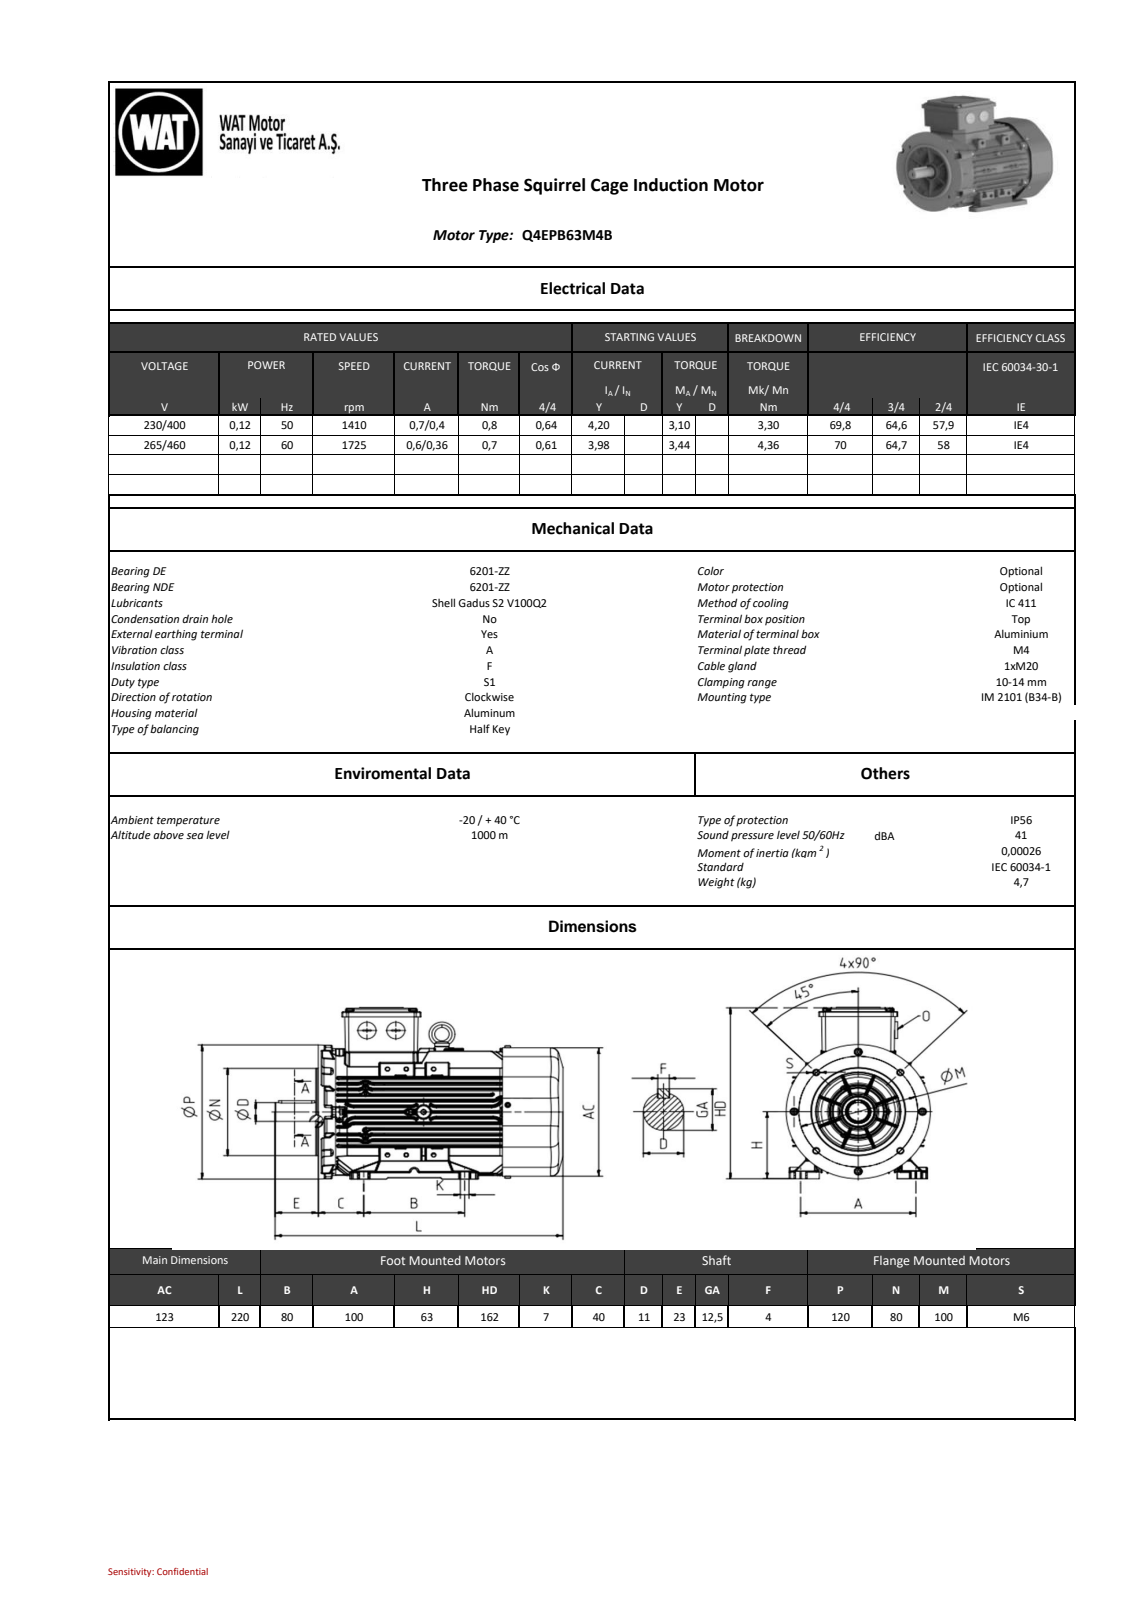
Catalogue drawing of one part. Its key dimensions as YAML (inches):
part_name: "QE series_ 63_B34b_stp_objects"
step_written_by: "SIEMENS PLM Software NX2206.8101 (AP203_CONFIGURATION_CONTROLLED_3D_DESIGN_OF_MECHANICAL_PARTS_AND_ASSEMBLIES_MIM_LF)"
units: inches
bodies: {solids: 0, faces: 1718, planar: 826, cylindrical: 557, other: 335}
overall_size: [8.64, 6.343, 5.039]
round_holes:
  - {diameter: 0.098, count: 4}
  - {diameter: 0.144, count: 4}
  - {diameter: 0.165, count: 4}
  - {diameter: 0.236, count: 4}
  - {diameter: 0.118, count: 2}
  - {diameter: 0.276, count: 2}
  - {diameter: 0.157, count: 1}
  - {diameter: 0.315, count: 1}
  - {diameter: 0.441, count: 1}
  - {diameter: 0.571, count: 1}
  - {diameter: 2.835, count: 1}
  - {diameter: 4.764, count: 1}
round_bosses_or_shafts:
  - {diameter: 0.315, count: 8}
  - {diameter: 0.157, count: 4}
  - {diameter: 4.843, count: 1}
  - {diameter: 4.724, count: 1}
  - {diameter: 3.15, count: 1}
  - {diameter: 1.024, count: 1}
  - {diameter: 0.748, count: 1}
partial_cylinders:
  - {radius: 0.02, count: 114}
  - {radius: 0.039, count: 99}
  - {radius: 0.079, count: 39}
  - {radius: 0.059, count: 28}
  - {radius: 0.004, count: 14}
  - {radius: 0.053, count: 12}
  - {radius: 0.157, count: 8}
  - {radius: 0.098, count: 7}
face_to_face_distances: [1.101, 0.079, 0.55, 0.557, 0.273, 0.236, 0.157, 0.271, 0.828, 0.276]
hole_center_spacings: [1.969, 2.126, 2.48, 2.784, 3.267, 0.394, 0.197, 0.803]
